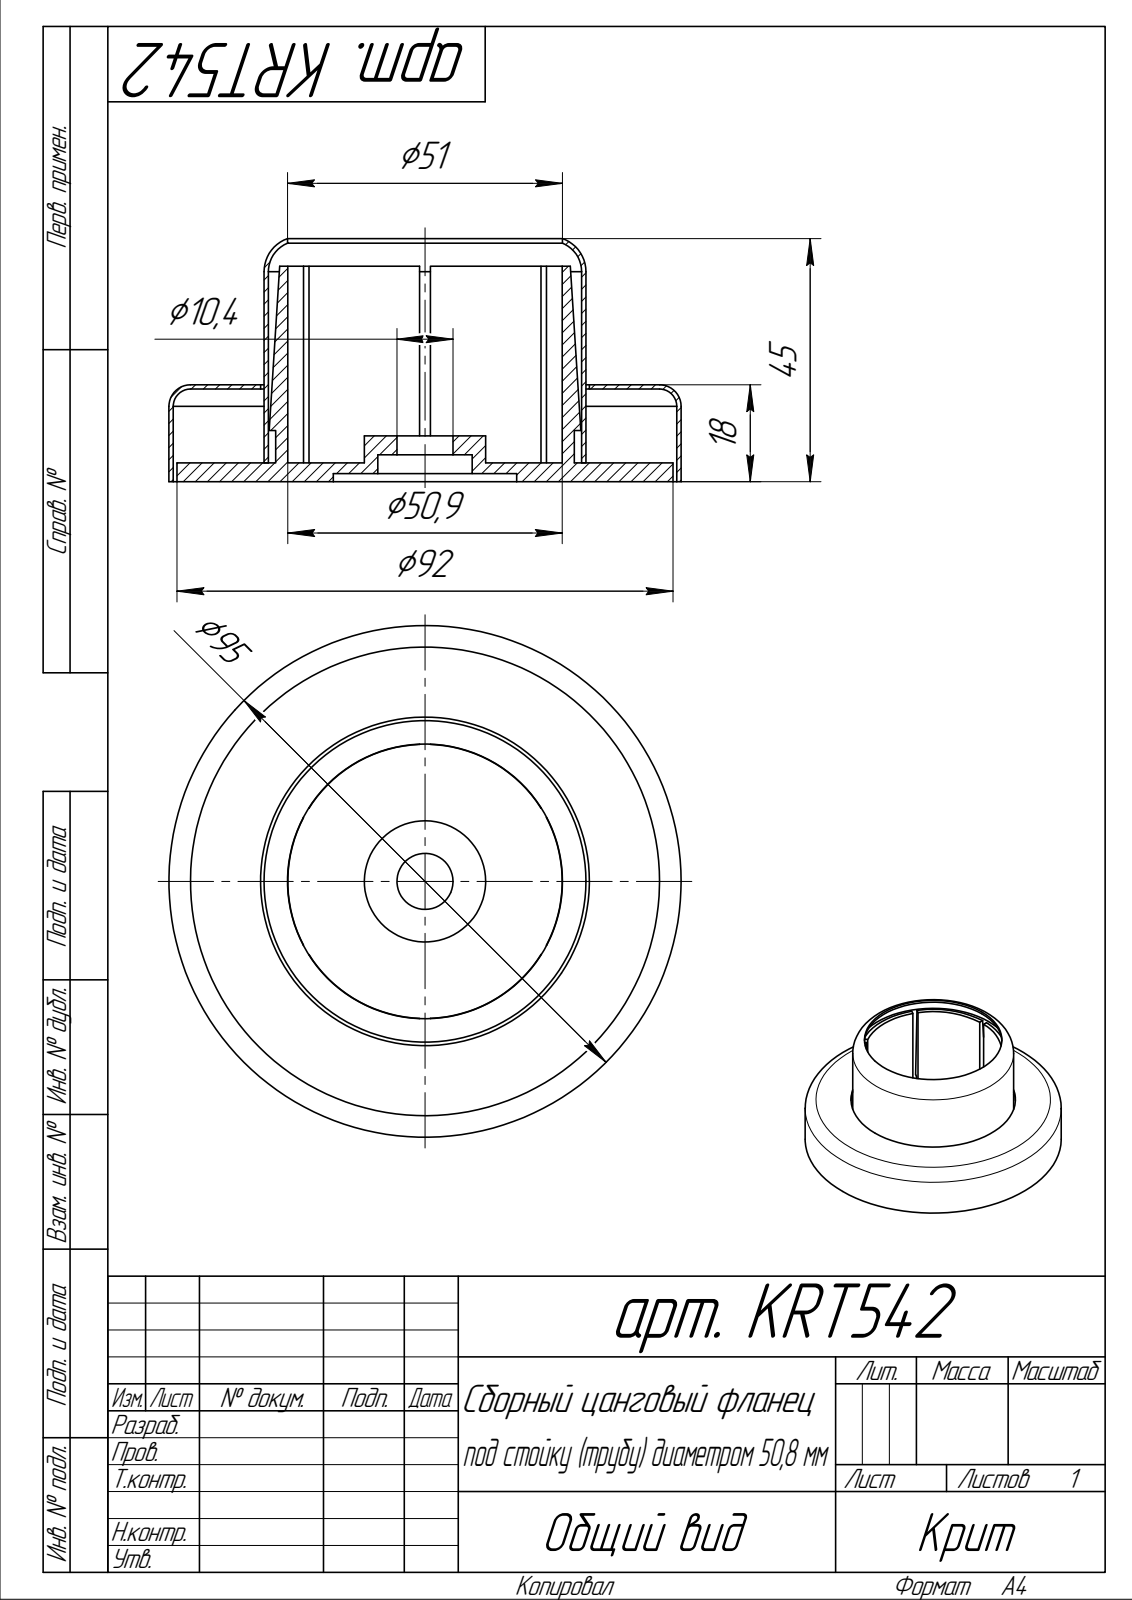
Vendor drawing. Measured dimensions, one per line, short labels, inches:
name: арт. KRT542; арт. KRT542.002; арт. KRT542.003; арт. KRT542.001
written by: SolidWorks 2014 (AUTOMOTIVE_DESIGN)
unit: in
bodies: 3 solids, 107 faces (39 planar, 53 cylindrical, 15 other)
size: 3.74 × 3.74 × 1.777
volume: 2.904 in³; area: 95.42 in²
holes: 3× ⌀0.256, 3× ⌀0.335, 1× ⌀0.409, 1× ⌀0.689, 1× ⌀2.004, 1× ⌀2.008, 1× ⌀2.287, 1× ⌀2.402, 1× ⌀3.677
bosses: 1× ⌀3.74, 1× ⌀3.622, 1× ⌀2.35, 1× ⌀2.181, 1× ⌀0.886
rounds: 4× R0.079, 1× R1.043
face distances: 0.138, 0.709, 0.677, 0.539, 0.571, 0.031, 0.079, 0.059, 0.618, 0.65
hole spacings: 1.496, 2.591, 2.992
